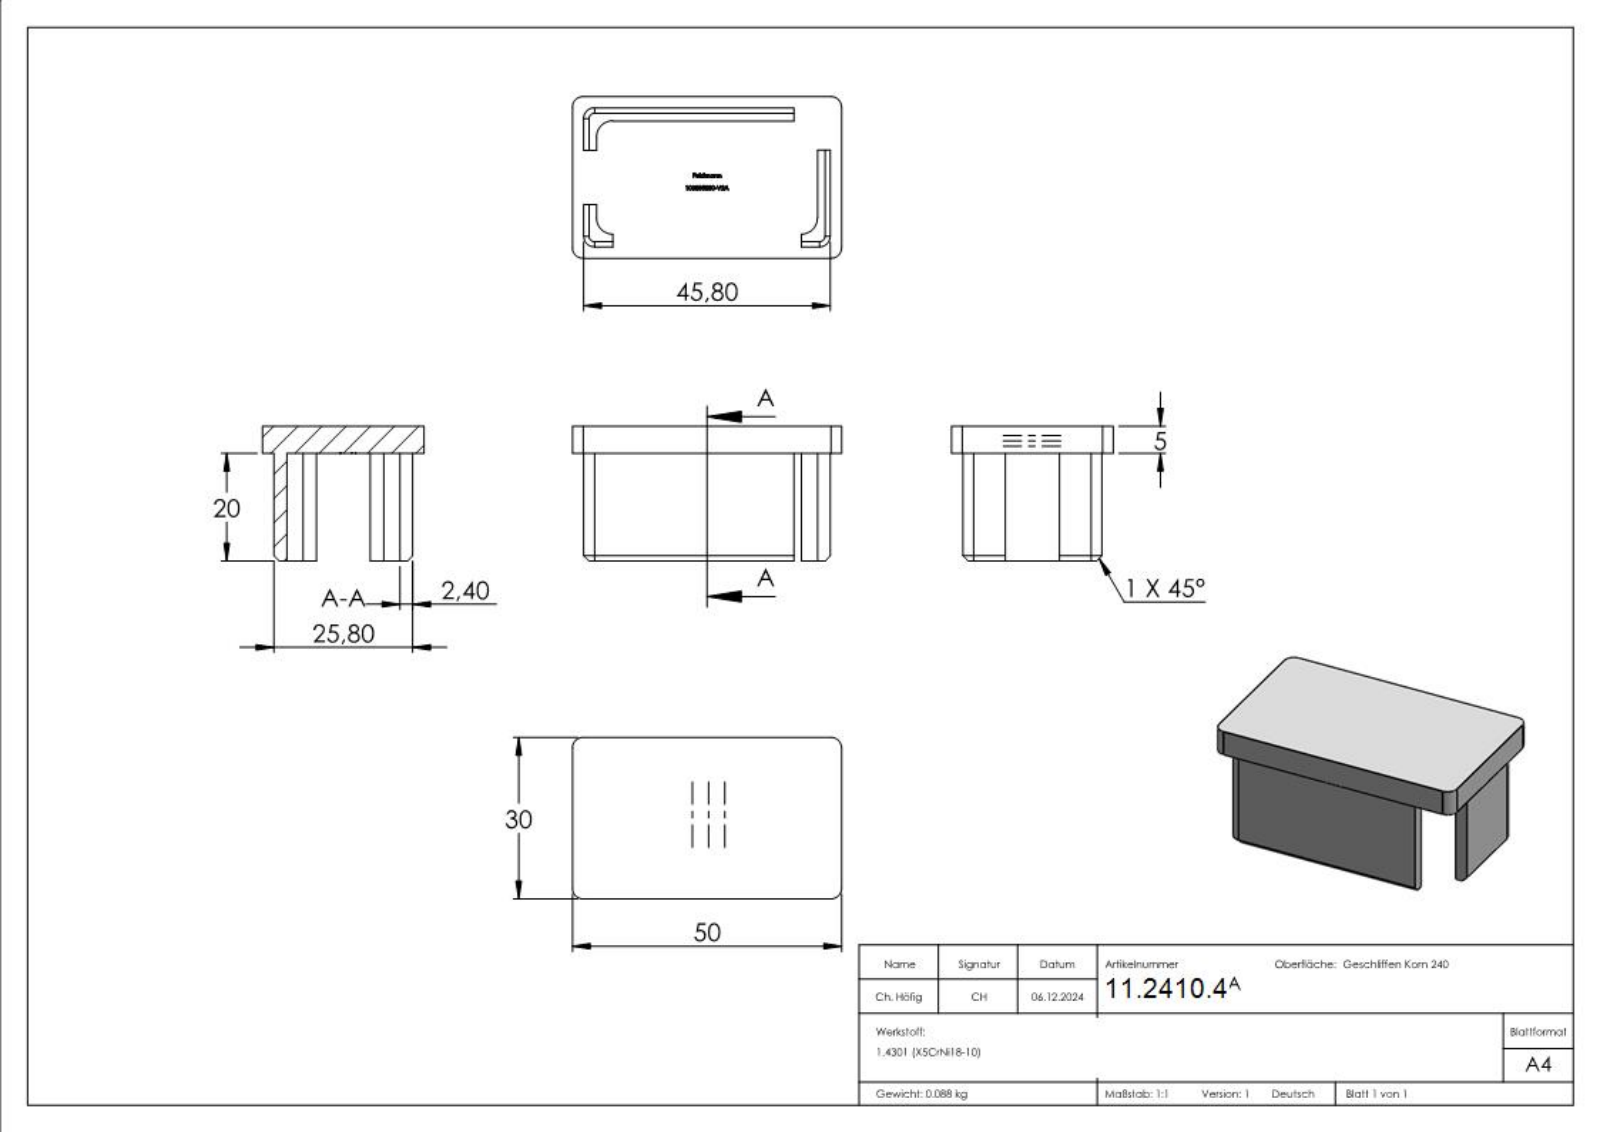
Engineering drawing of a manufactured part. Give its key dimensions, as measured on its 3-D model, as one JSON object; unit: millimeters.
{"part_name": "100035030-V2A", "step_written_by": "SolidWorks 2018 (CONFIG_CONTROL_DESIGN)", "units": "millimeters", "bodies": {"solids": 1, "faces": 309, "planar": 161, "cylindrical": 10, "other": 138}, "overall_size": [50, 30, 25], "volume_mm3": 11174, "surface_area_mm2": 6947, "partial_cylinders_radius": [[2, 7], [3, 3]], "face_to_face_distances": [5, 2.4, 2.1, 4.5, 27.9, 43.4, 47.9, 45.5, 25.5, 30]}
